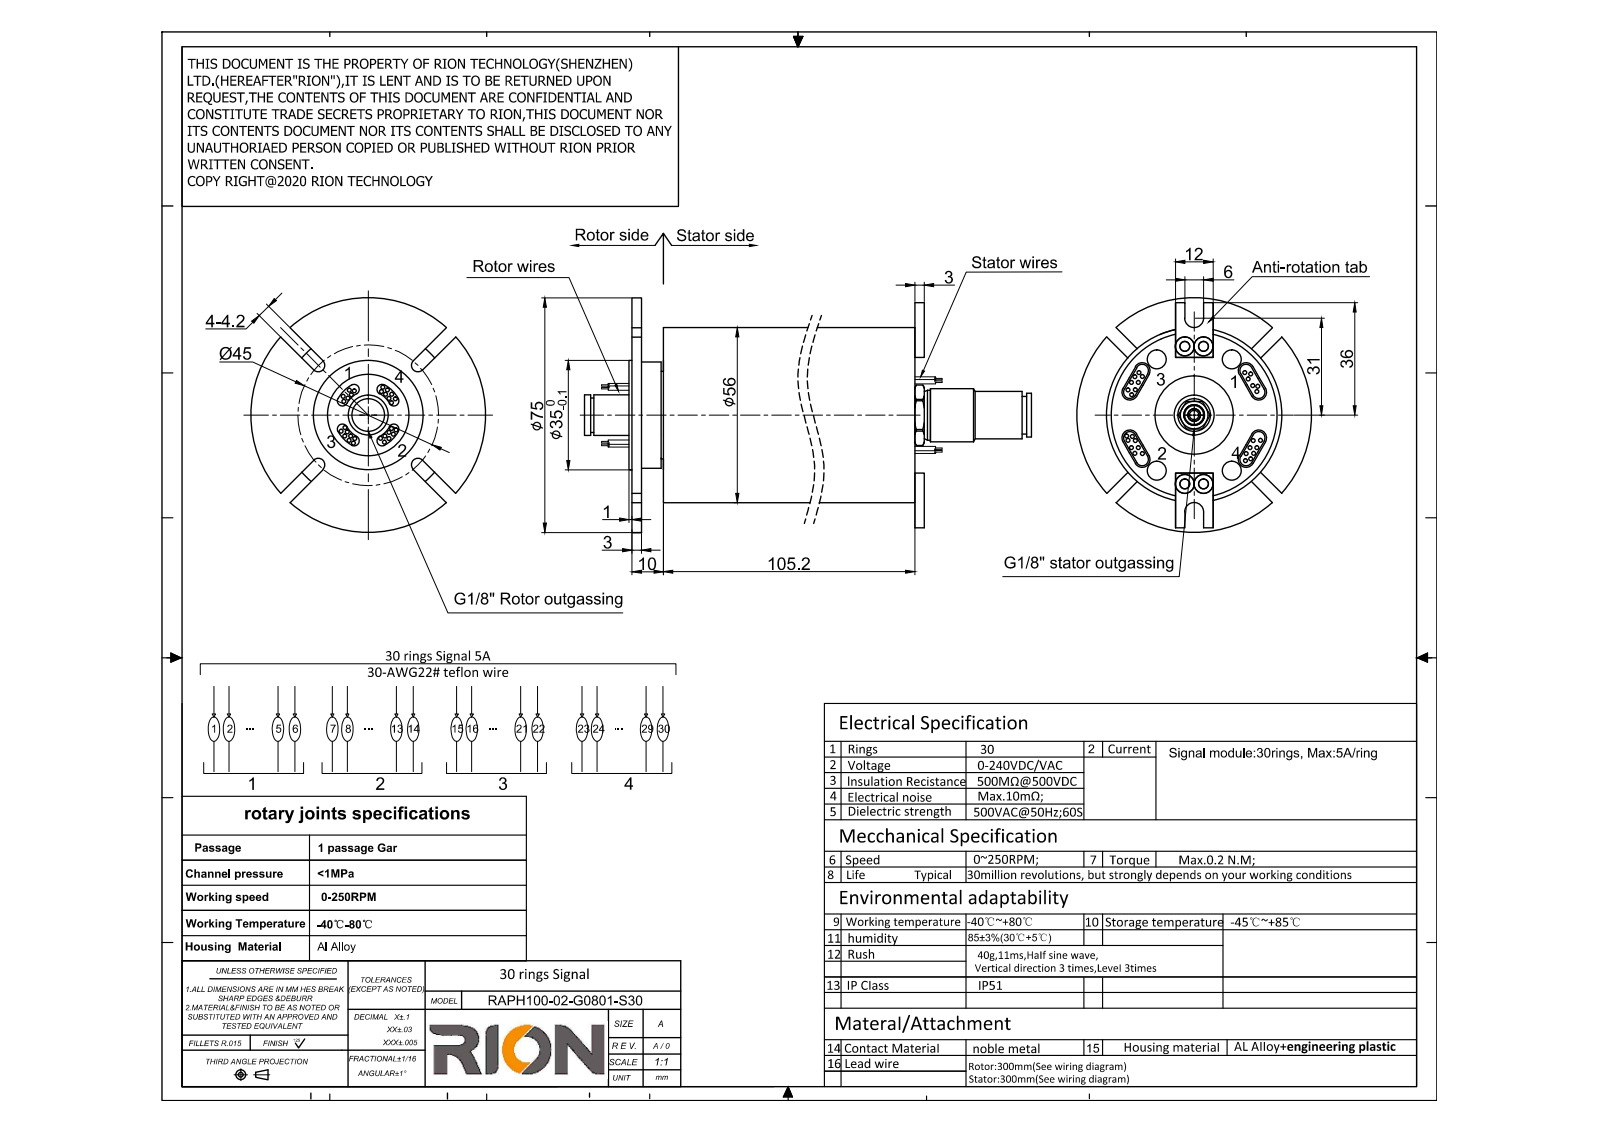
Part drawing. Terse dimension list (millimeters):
name: RAPH100-02-G0801-S30; KSH08-01S; MAPH100-02-S30; KQ2S08-01S
written by: SolidWorks 2014 (CONFIG_CONTROL_DESIGN)
unit: mm
bodies: 3 solids, 444 faces (158 planar, 246 cylindrical, 40 other)
size: 166.4 × 75 × 75
volume: 281 876 mm³; area: 48 668 mm²
holes: 4× ⌀2.5, 4× ⌀3.2, 1× ⌀6, 1× ⌀8, 1× ⌀8.8, 1× ⌀9, 1× ⌀12.7, 1× ⌀17.2, 1× ⌀26, 1× ⌀53
bosses: 60× ⌀1.3, 1× ⌀75, 1× ⌀56, 1× ⌀52.8, 1× ⌀35, 1× ⌀34, 1× ⌀28, 1× ⌀17
rounds: 8× R1.62, 8× R2, 4× R2.1, 2× R3, 1× R7.75, 1× R11
face distances: 3, 115.2, 112.2, 10, 7, 105.2, 11, 5.3, 4, 4.3
hole spacings: 22.2, 6, 44, 44.41
